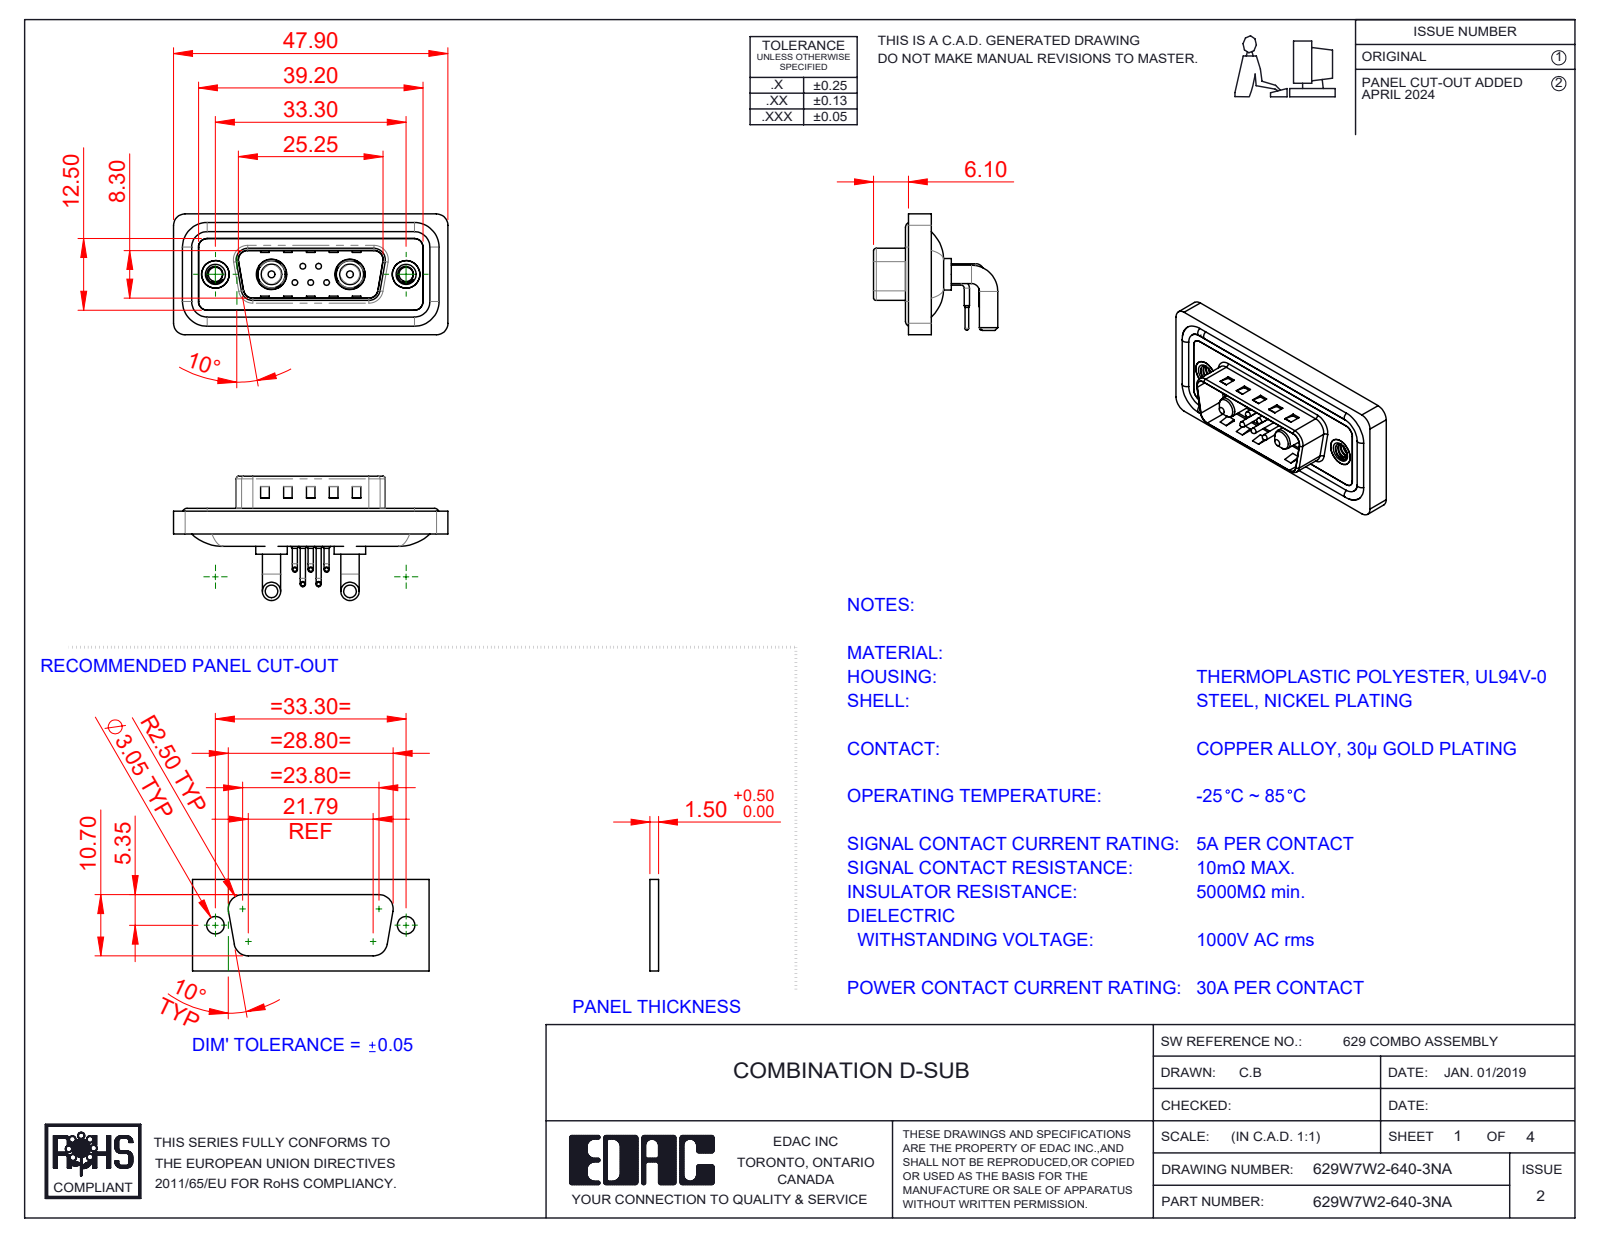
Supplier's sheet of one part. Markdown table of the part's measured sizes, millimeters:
| quantity | value |
| --- | --- |
| part name | 629Combo Waterproof Housing_15 Contacts; 629Combo Threaded Rivet_A; 629Combo Housing_7W2; 629Combo Shell Rear_15 Contacts (+5 more) |
| STEP written by | SolidWorks 2023 (CONFIG_CONTROL_DESIGN) |
| units | millimeters |
| bodies | 16 solids, 1077 faces (517 planar, 404 cylindrical, 156 other) |
| overall size | 47.9 × 21.7 × 21.1 |
| volume | 5 740 mm³ |
| surface area | 9 181 mm² |
| round holes (diameter × count) | 0.75 × 5, 1.6 × 5, 2 × 5, 2.5 × 2, 4 × 2, 4.8 × 2, 4.85 × 2, 5 × 2, 5.3 × 2 |
| round bosses / shafts (diameter × count) | 0.9 × 10, 1.5 × 5, 1 × 5, 0.65 × 5, 3.2 × 4, 1.6 × 4, 5.5 × 2, 5.2 × 2 |
| partial cylindrical surfaces (radius × count) | 2 × 20, 1.5 × 18, 0.5 × 8, 1.6 × 8, 1.01 × 5, 0.25 × 4, 0.6 × 4, 0.65 × 4 |
| main face-to-face distances | 0.4, 2.9, 0.8, 1.1, 2.1, 1.6, 2.5, 3.1, 4.5, 4.1 |
| hole center spacings | 3.16, 2.77, 9.8, 23.5, 4.31, 4.33, 5.03, 5.04 |
